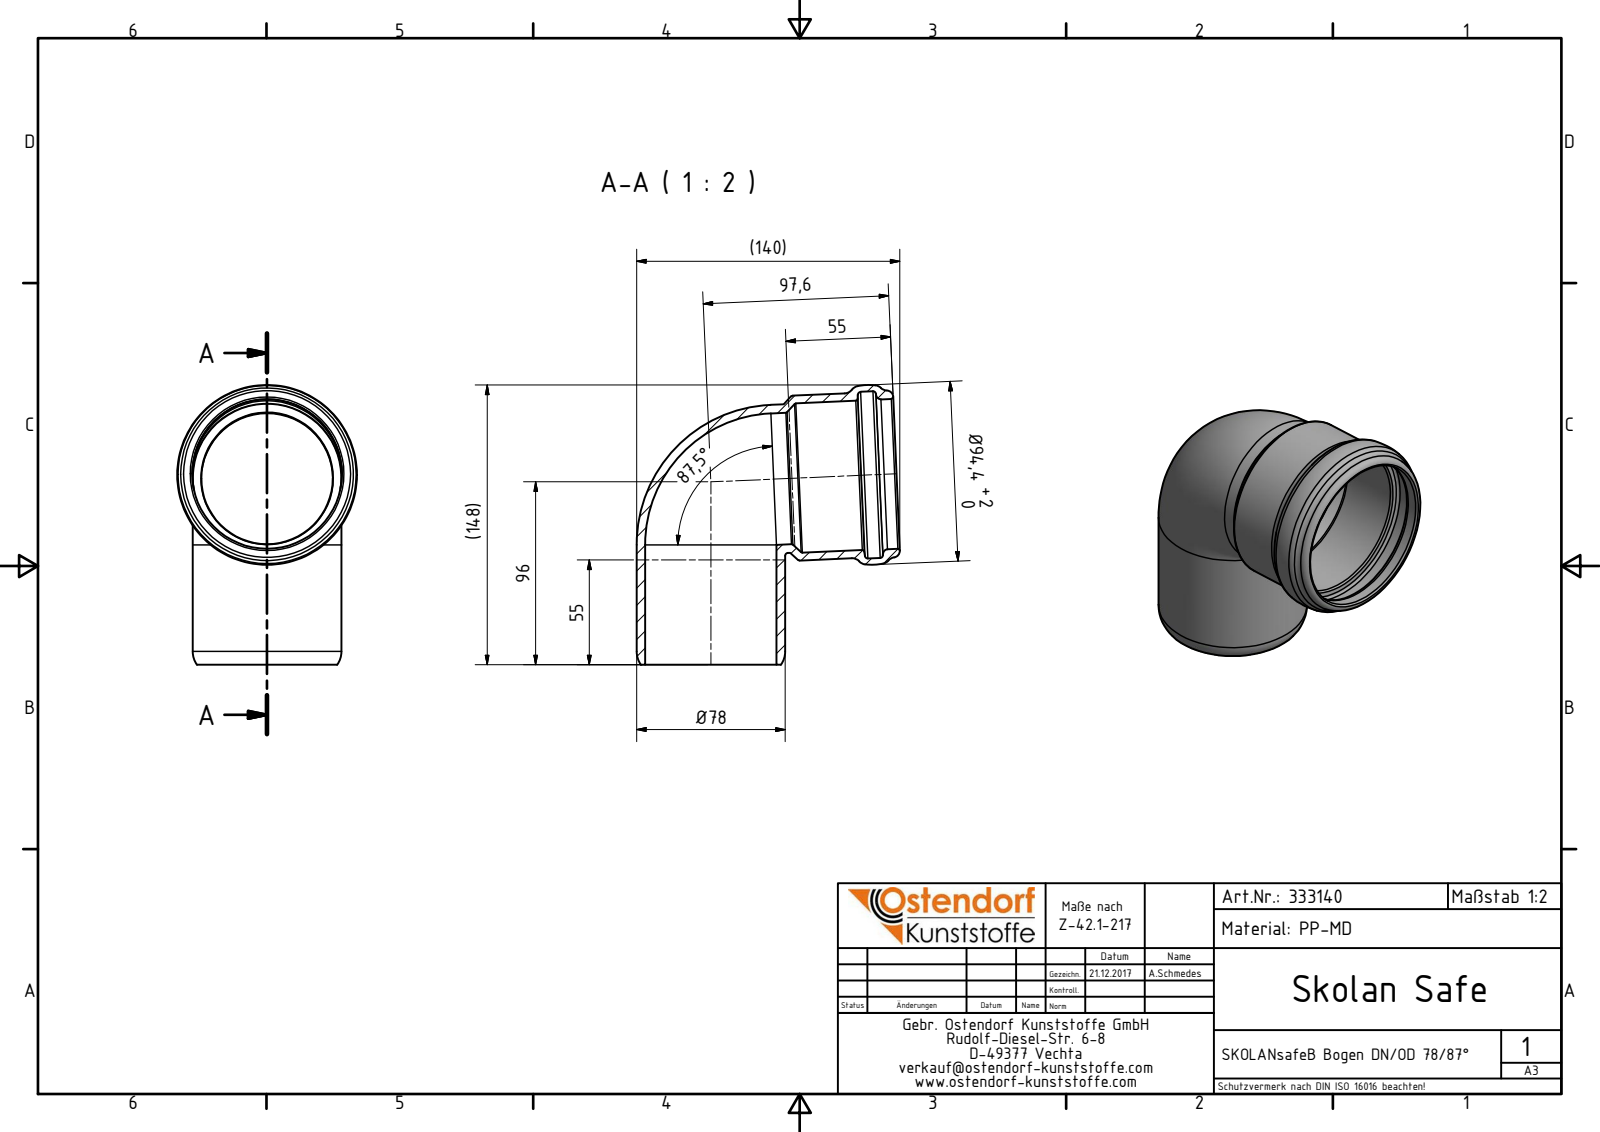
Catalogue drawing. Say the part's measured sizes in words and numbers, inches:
The part is named "333140 SKOLANsafeB Bogen DN_OD 78_87°". Its 3-D file was written by "Autodesk Inventor 2016 (AUTOMOTIVE_DESIGN)". It is 1 solid with 31 faces: 1 planar, 8 cylindrical and 22 other. Overall it measures 5.781 by 5.444 by 3.717 inches. Its volume is 11.54 cubic inches and its surface area 141.4 square inches. Round holes: 2 of diameter 2.717, 1 of diameter 3.087, 1 of diameter 3.098, 1 of diameter 3.449. Round bosses or shafts: 2 of diameter 3.071, 1 of diameter 3.409.
